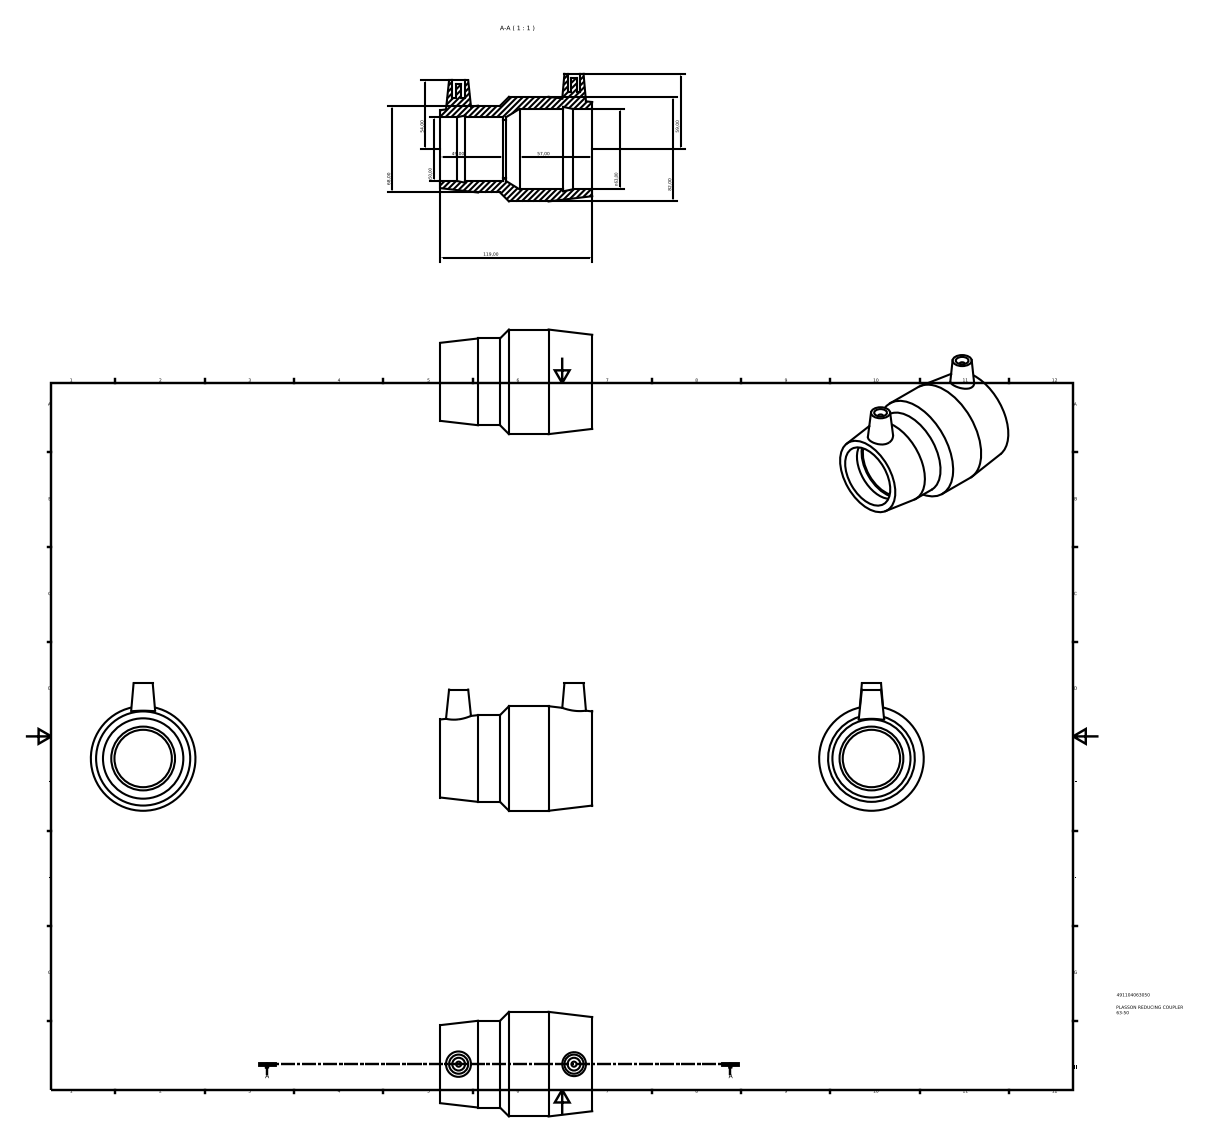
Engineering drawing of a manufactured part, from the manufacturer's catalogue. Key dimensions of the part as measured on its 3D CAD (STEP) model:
Part name (STEP PRODUCT): 491104063050
STEP written by: Autodesk Inventor 2015 (AUTOMOTIVE_DESIGN)
Units: millimetres
Bodies: 1 solid, 31 faces (12 planar, 11 cylindrical, 8 other)
Overall size (bounding box): 119 × 100 × 82
Volume: 219 263 mm³ · Surface area: 56 831 mm²
Round holes (diameter × count): ⌀10 ×2, ⌀45 ×1, ⌀50 ×1, ⌀63 ×1
Round bosses / shafts (diameter × count): ⌀4 ×2, ⌀82 ×1, ⌀68 ×1
Main face-to-face distances: 119, 51.45, 67.55, 49, 2.45, 70, 96.2, 47.2, 44.75, 22.8
Hole centre spacings: 90.44
